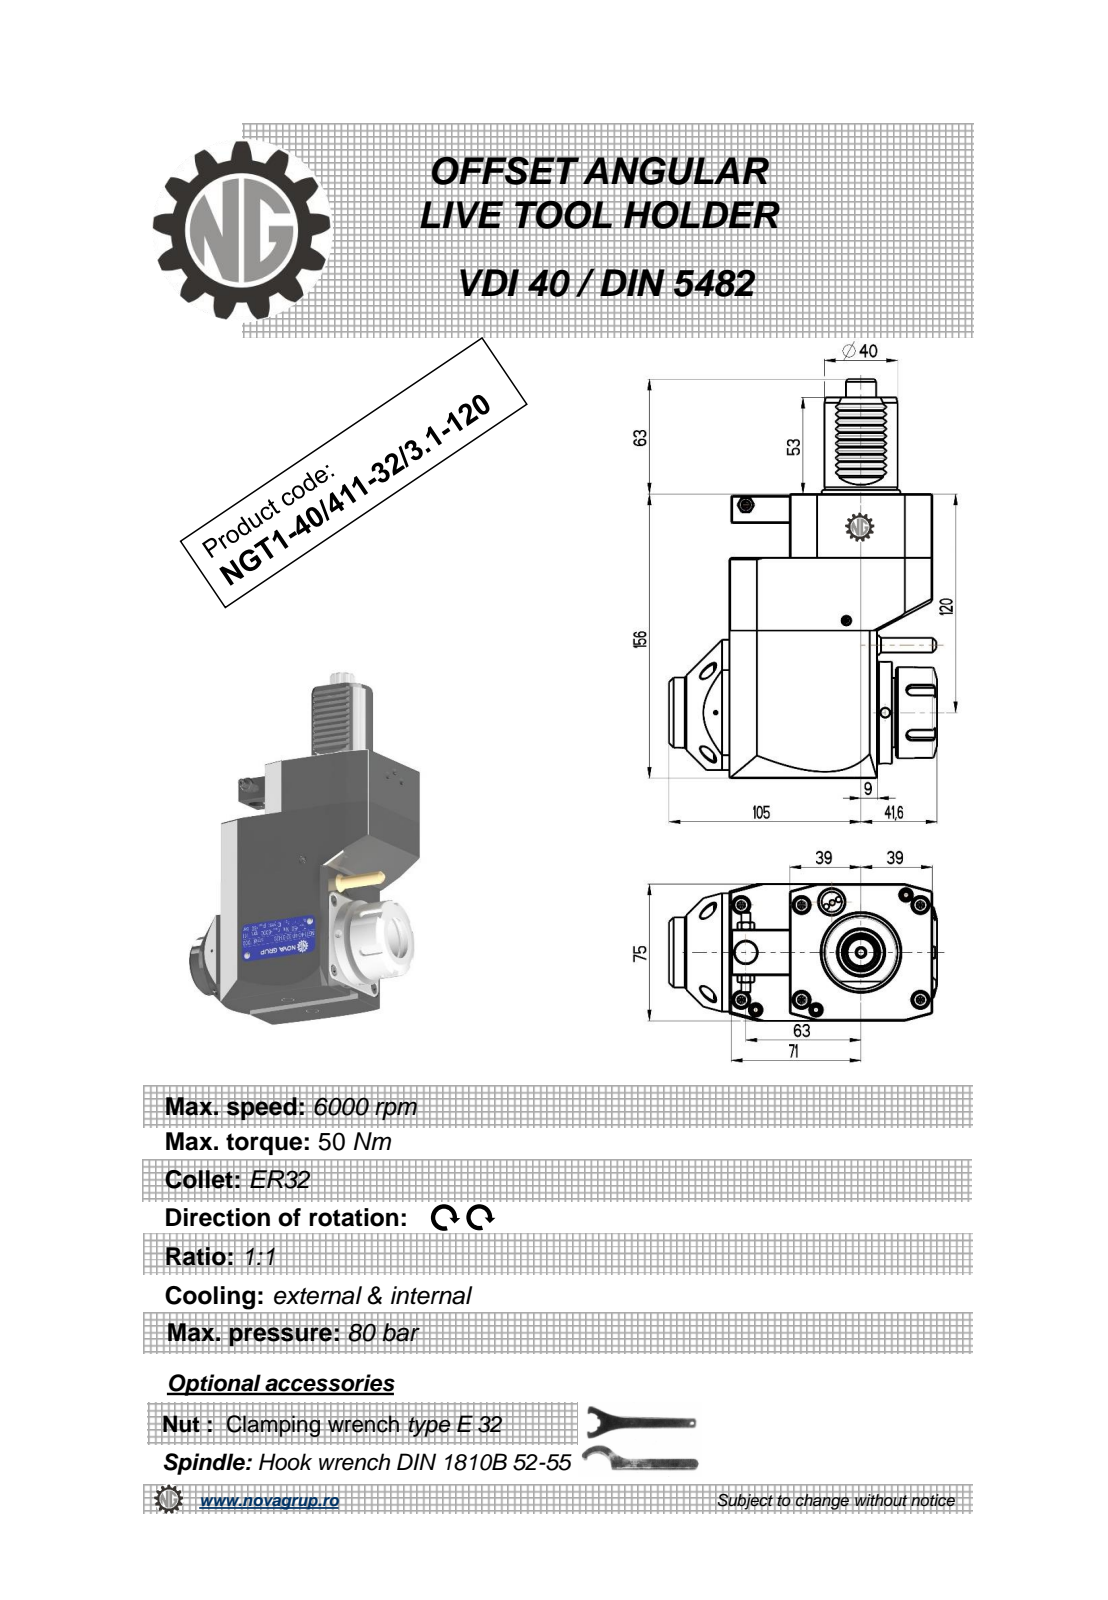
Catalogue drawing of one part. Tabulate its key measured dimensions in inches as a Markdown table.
| quantity | value |
| --- | --- |
| part name | NGT1_40_411_32_3_1_120 |
| STEP written by | PRO/ENGINEER BY PARAMETRIC TECHNOLOGY CORPORATION, 2010280 (CONFIG_CONTROL_DESIGN) |
| units | inches |
| bodies | 1 solid, 471 faces (197 planar, 122 cylindrical, 152 other) |
| overall size | 8.622 × 5.772 × 2.953 |
| volume | 73.96 in³ |
| surface area | 138.9 in² |
| round holes (diameter × count) | 0.197 × 3, 0.165 × 2, 0.118 × 1, 0.374 × 1, 0.472 × 1, 1.063 × 1 |
| round bosses / shafts (diameter × count) | 2.205 × 1, 1.969 × 1, 1.693 × 1, 1.575 × 1, 1.516 × 1, 0.441 × 1, 0.353 × 1, 0.315 × 1 |
| partial cylindrical surfaces (radius × count) | 0.119 × 18, 0.01 × 12, 0.012 × 10, 0.009 × 6, 0.118 × 5, 0.02 × 1, 0.266 × 1, 0.325 × 1 |
| main face-to-face distances | 2.953, 6.142, 4.37, 1.299, 1.378, 4.764, 3.189, 1.181, 1.89, 3.071 |
| hole center spacings | 0.522, 1.611, 2.48, 3.002, 3.051, 4.429, 5.4 |
